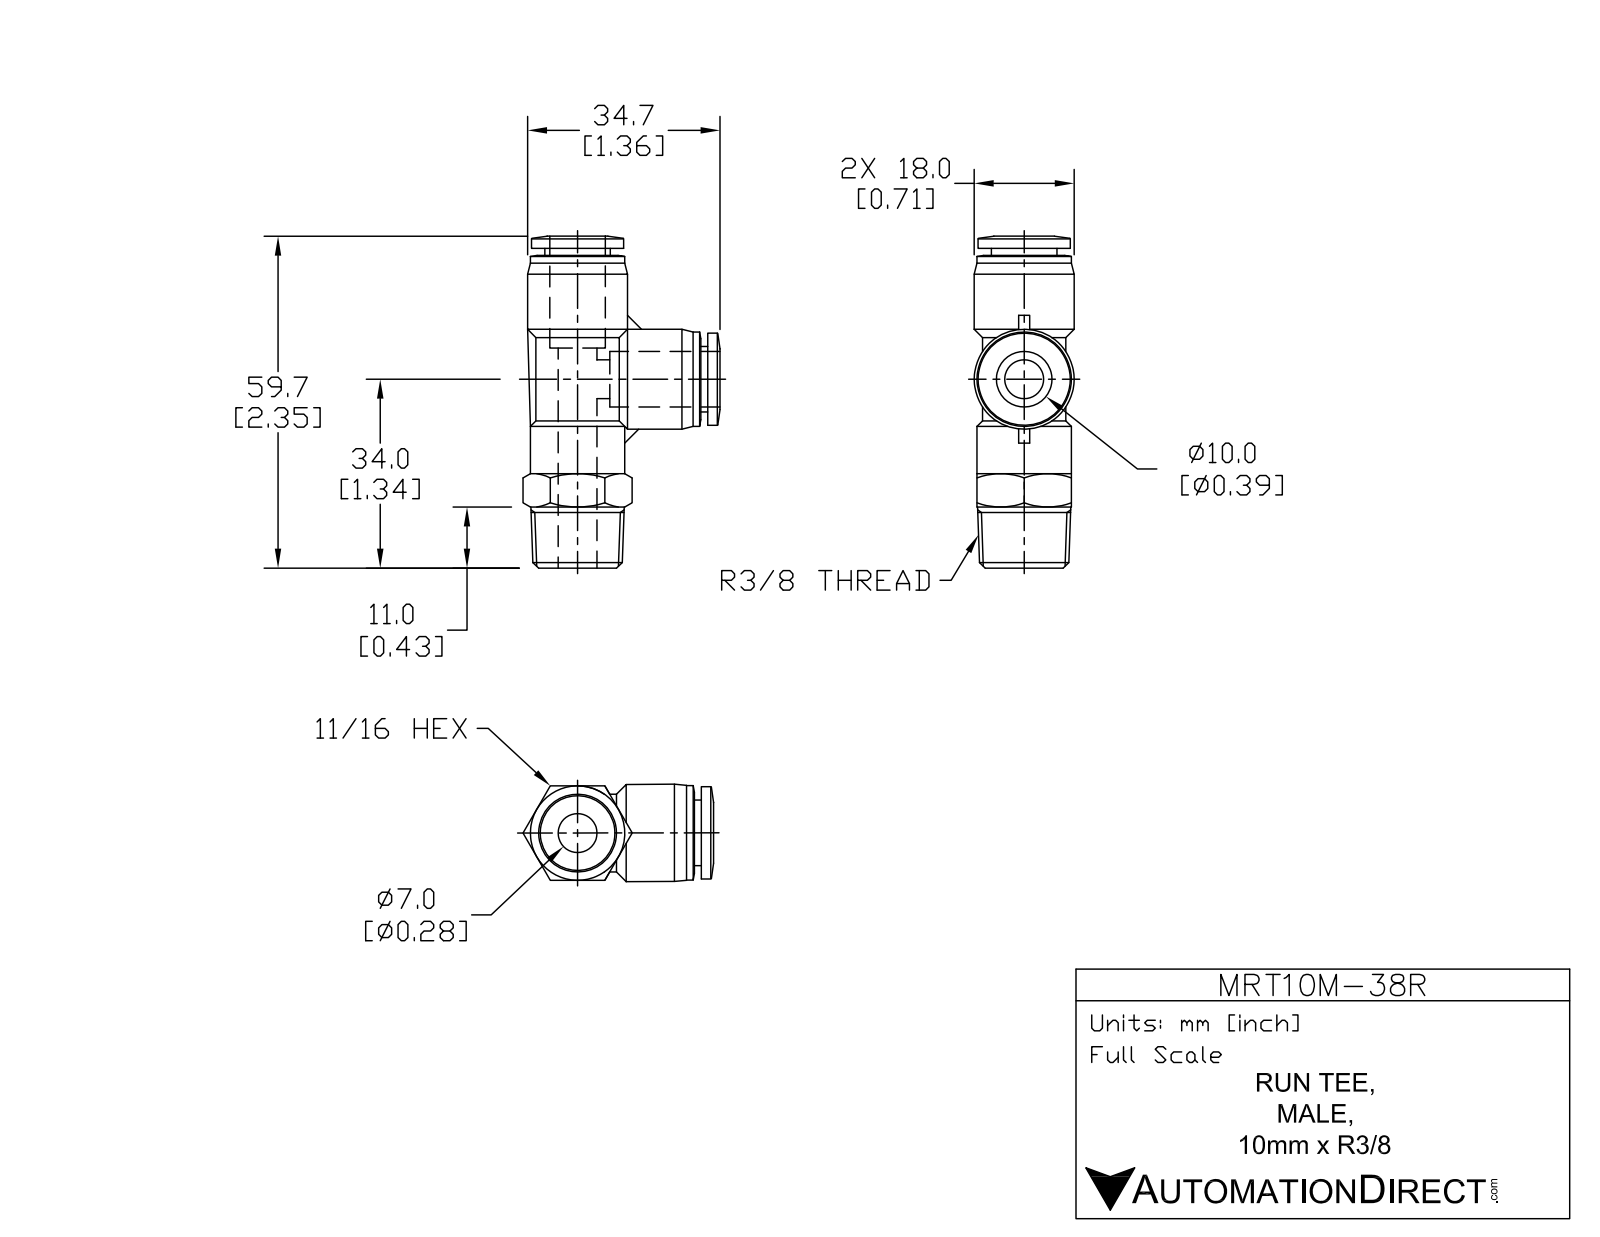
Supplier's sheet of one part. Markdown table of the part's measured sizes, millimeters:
| quantity | value |
| --- | --- |
| part name | MRT10M-38R |
| STEP written by | SolidWorks 2015 (AUTOMOTIVE_DESIGN) |
| units | millimeters |
| bodies | 1 solid, 103 faces (24 planar, 32 cylindrical, 47 other) |
| overall size | 59.7 × 35.6 × 18 |
| volume | 11 800 mm³ |
| surface area | 7 303 mm² |
| round holes (diameter × count) | 8 × 2, 10.3 × 2 |
| round bosses / shafts (diameter × count) | 18 × 2, 17 × 2, 16.6 × 2, 15 × 2, 11.8 × 2 |
| main face-to-face distances | 17, 1.2, 57.6, 16.7, 18, 56.3, 7.5, 9.5, 39.5, 2 |
